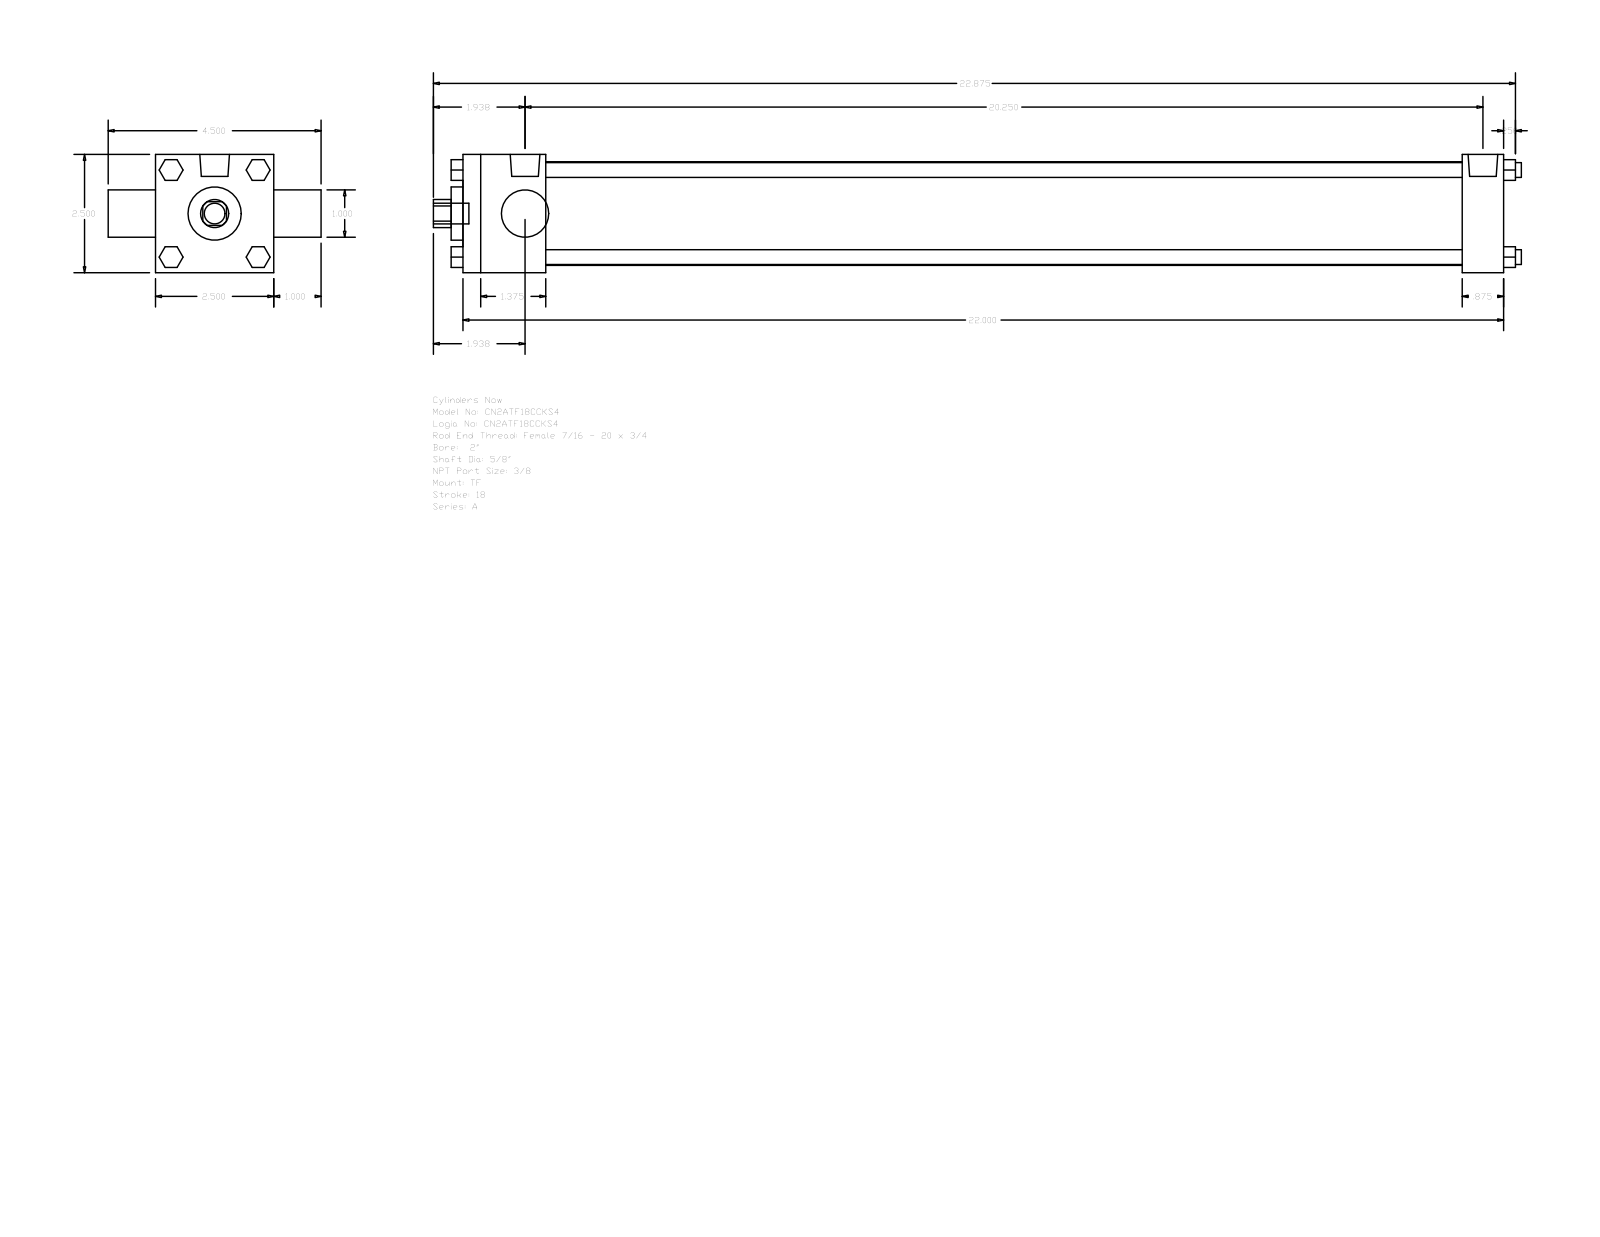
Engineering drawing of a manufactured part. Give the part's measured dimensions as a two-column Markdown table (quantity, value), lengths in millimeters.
| quantity | value |
| --- | --- |
| part name | A_TF__0200_0.625 |
| STEP written by | GSSL Pune (CONFIG_CONTROL_DESIGN) |
| units | millimeters |
| bodies | 0 solids, 120 faces (92 planar, 28 cylindrical, 0 other) |
| overall size | 584.2 × 114.3 × 63.5 |
| round holes (diameter × count) | 15.88 × 1, 25.4 × 1, 28.57 × 1, 55.63 × 1 |
| round bosses / shafts (diameter × count) | 7.94 × 4, 5.56 × 3, 15.93 × 2, 11.11 × 1 |
| partial cylindrical surfaces (radius × count) | 7.54 × 1 |
| main face-to-face distances | 63.5, 558.79, 44.45, 536.57, 492.12, 514.34, 22.22, 25.4, 88.9, 6.35 |
